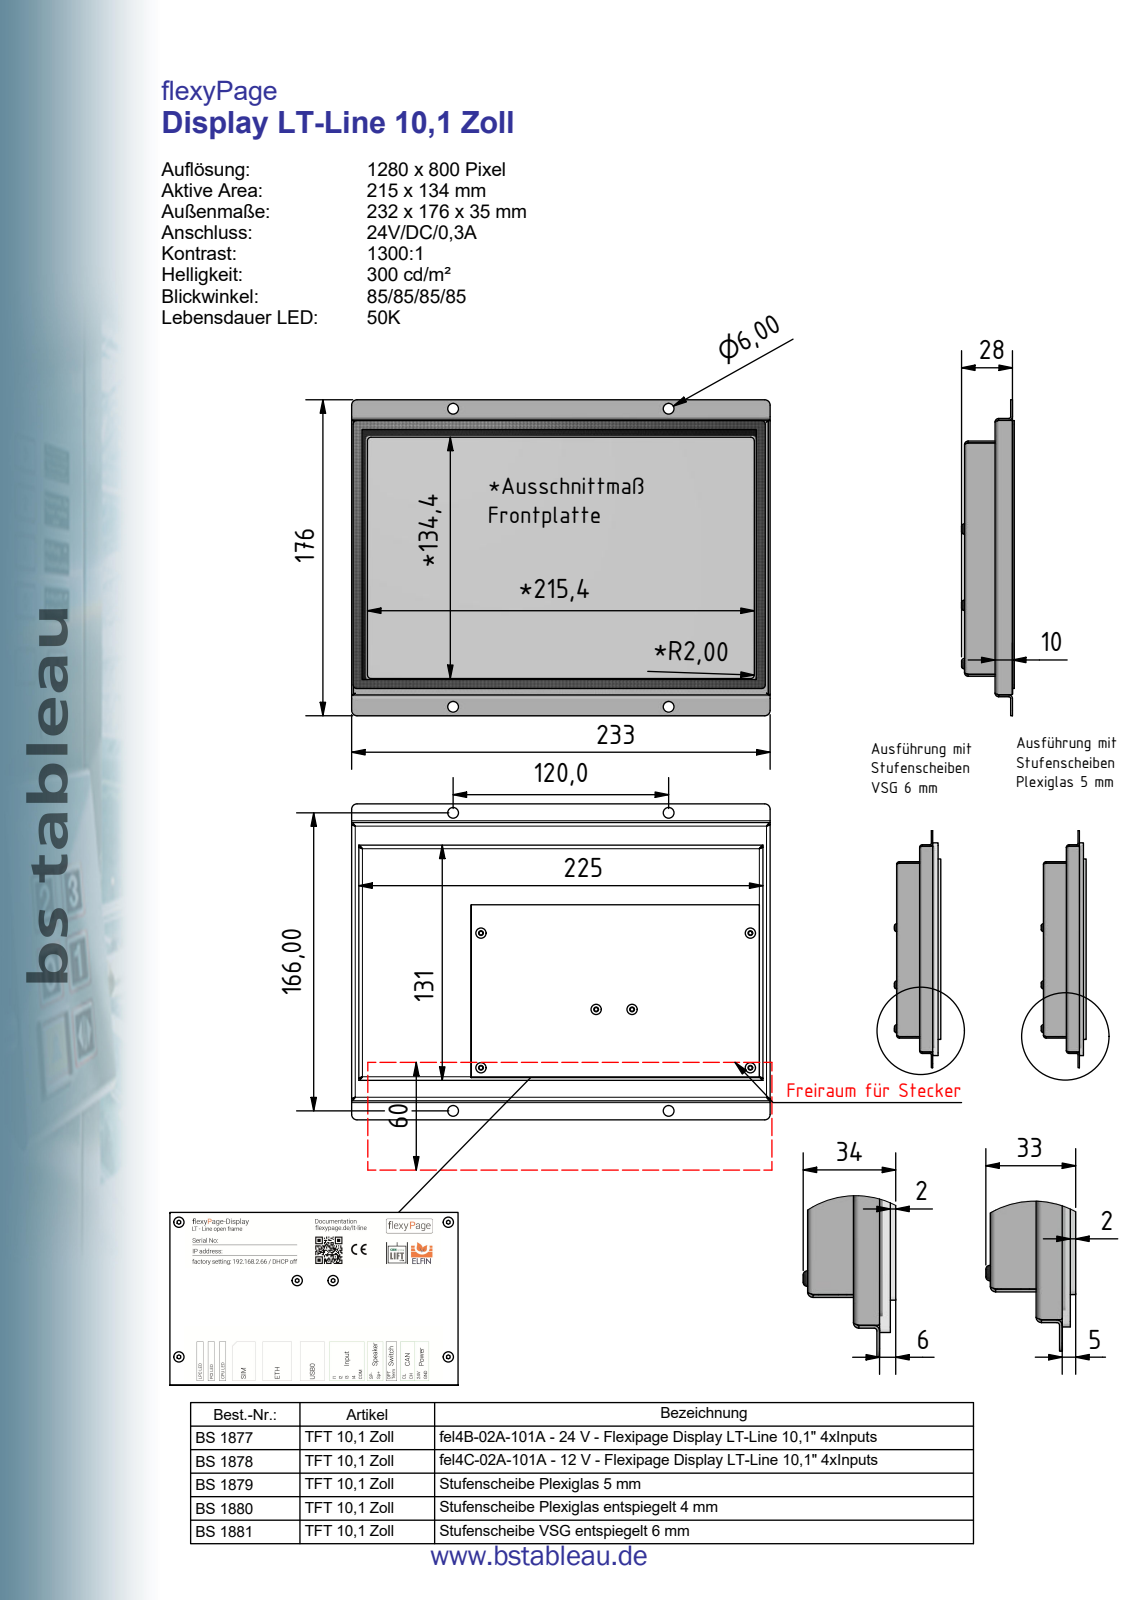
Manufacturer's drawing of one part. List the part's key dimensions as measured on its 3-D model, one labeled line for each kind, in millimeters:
Part name (STEP PRODUCT): 00004930 fel4B-02A-10,1 Zoll LT-Line
STEP written by: Autodesk Inventor 2019 (AUTOMOTIVE_DESIGN)
Units: millimetres
Bodies: 28 solids, 1486 faces (864 planar, 189 cylindrical, 433 other)
Overall size (bounding box): 233 × 176 × 29.35
Volume: 311 590 mm³ · Surface area: 279 887 mm²
Round holes (diameter × count): ⌀1.4 ×4, ⌀2.2 ×4, ⌀2.46 ×4, ⌀3.45 ×4, ⌀4.4 ×4, ⌀5.41 ×4, ⌀6 ×4, ⌀1.5 ×3, ⌀3.1 ×2
Round bosses / shafts (diameter × count): ⌀0.4 ×11, ⌀5.7 ×6, ⌀3 ×6, ⌀5.42 ×4, ⌀2 ×4
Partial cylindrical surfaces — rounded edges, fillets, slot ends (radius × count): R1.5 ×24, R2 ×23, R0.3 ×21, R1 ×10, R0.6 ×9, R0.2 ×8, R0.5 ×8, R3 ×4
Main face-to-face distances: 1, 17, 8.7, 5.54, 9.7, 25.7, 26.7, 3.16, 18, 4.16
Hole centre spacings: 6, 52.84, 53.42, 68.76, 75, 105, 120, 141.83
